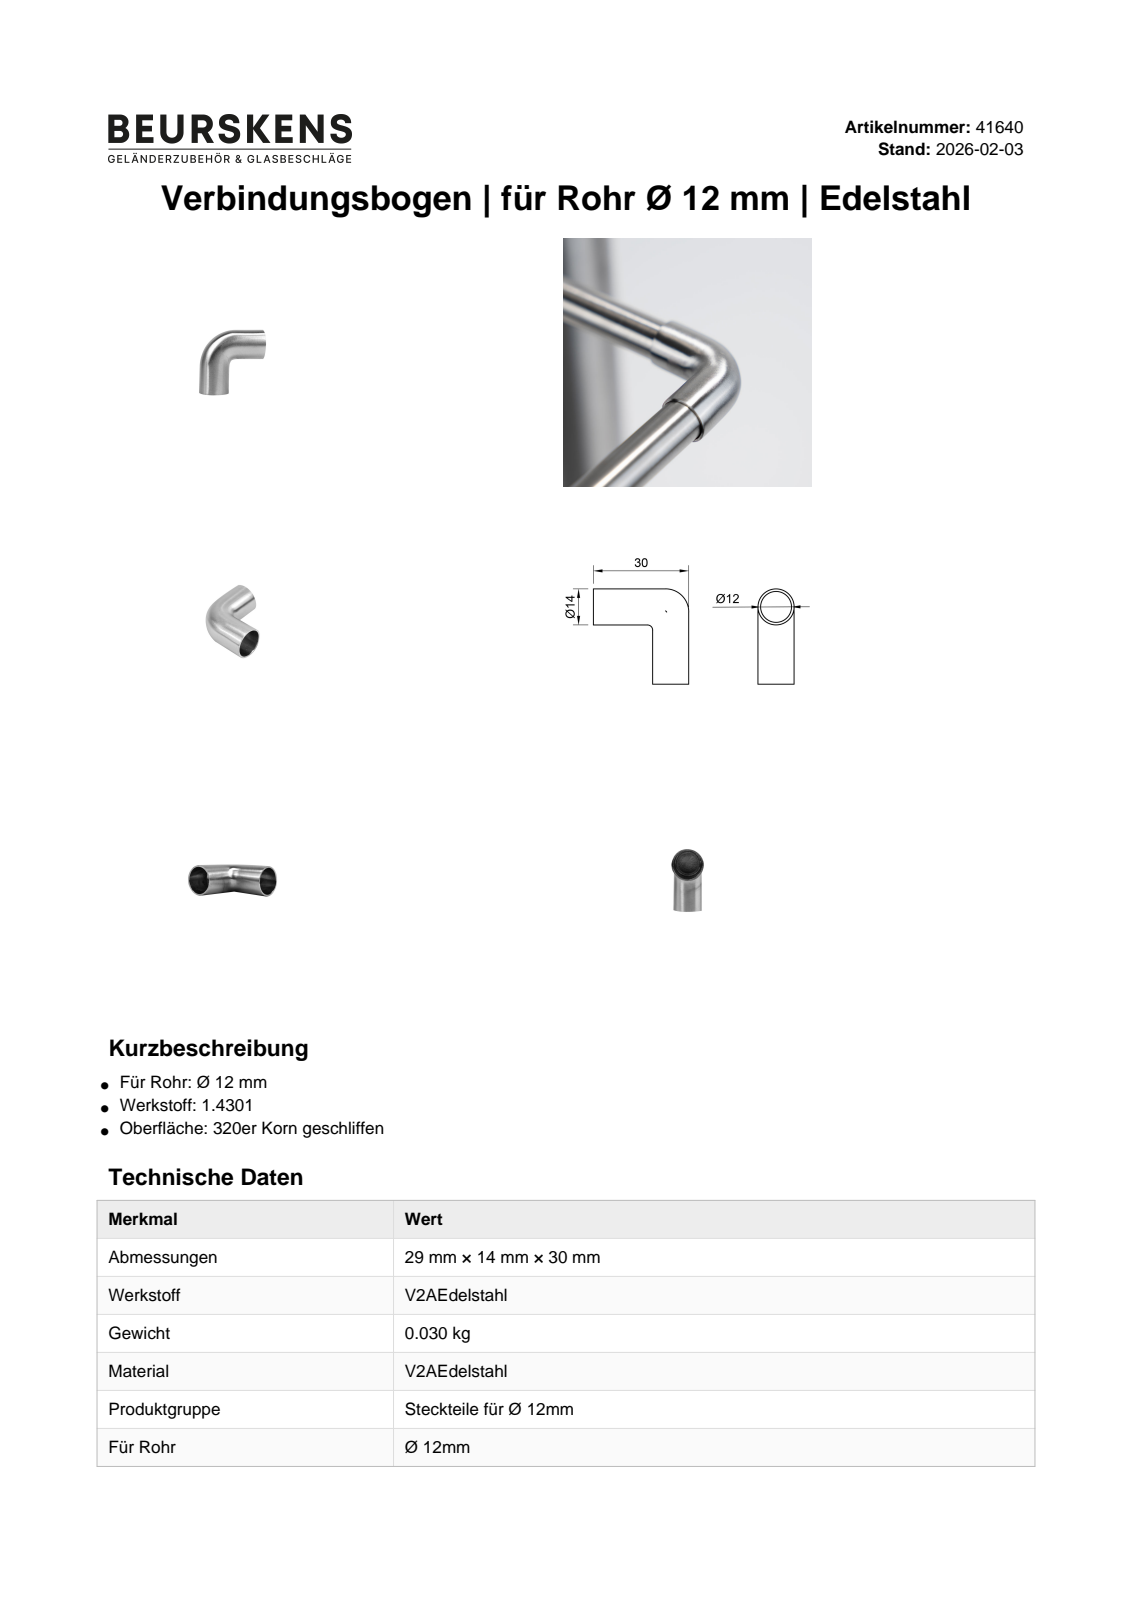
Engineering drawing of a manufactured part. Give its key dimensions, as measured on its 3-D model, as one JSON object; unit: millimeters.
{"part_name": "41640", "step_written_by": "Autodesk Inventor 2022 (AUTOMOTIVE_DESIGN)", "units": "millimeters", "bodies": {"solids": 1, "faces": 10, "planar": 2, "cylindrical": 4, "other": 4}, "overall_size": [37, 37, 14], "volume_mm3": 5629, "surface_area_mm2": 3971, "round_holes": [[12, 2]], "round_bosses_or_shafts": [[14, 2]]}
